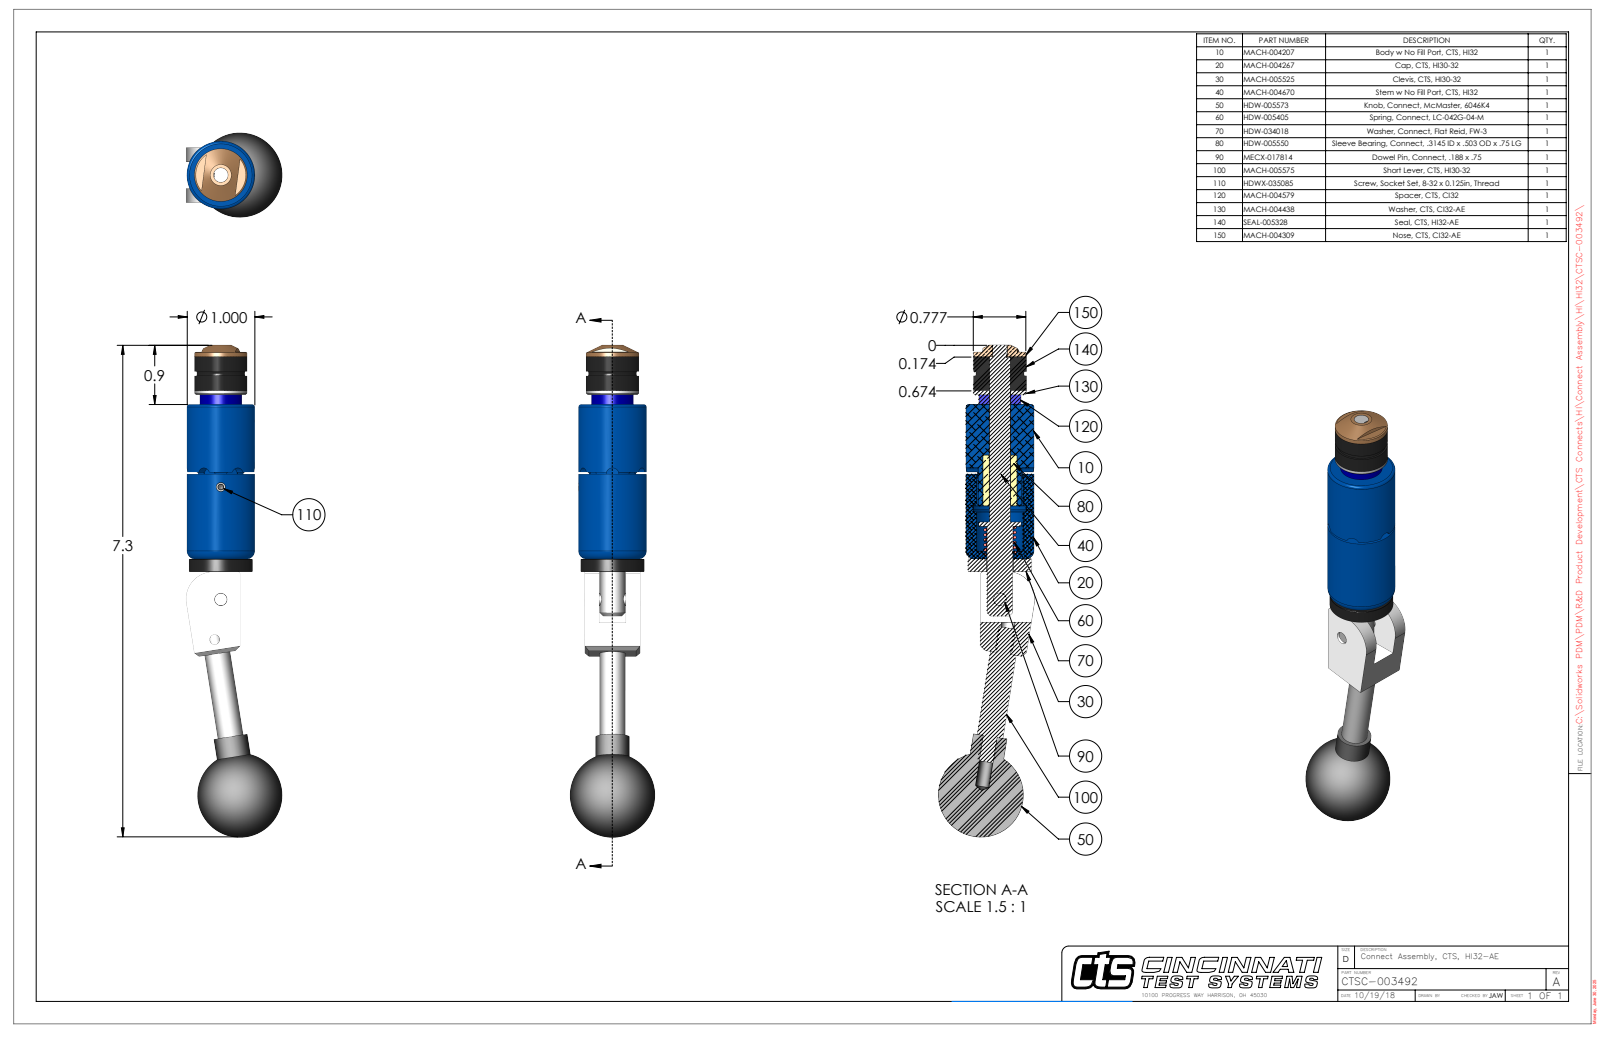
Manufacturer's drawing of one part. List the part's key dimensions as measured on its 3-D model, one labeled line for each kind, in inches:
Part name (STEP PRODUCT): CTSC-003492
STEP written by: SolidWorks 2023 (AUTOMOTIVE_DESIGN)
Units: inches
Bodies: 10 solids, 254 faces (97 planar, 100 cylindrical, 57 other)
Overall size (bounding box): 7.268 × 1.416 × 1.25
Volume: 4.009 in³ · Surface area: 34.63 in²
Round holes (diameter × count): ⌀0.201 ×2, ⌀0.136 ×1, ⌀0.15 ×1, ⌀0.189 ×1, ⌀0.213 ×1, ⌀0.31 ×1, ⌀0.314 ×1, ⌀0.316 ×1, ⌀0.385 ×1, ⌀0.392 ×1
Round bosses / shafts (diameter × count): ⌀0.25 ×2, ⌀0.201 ×2, ⌀1 ×1, ⌀0.936 ×1, ⌀0.777 ×1, ⌀0.618 ×1, ⌀0.5 ×1, ⌀0.38 ×1
Partial cylindrical surfaces — rounded edges, fillets, slot ends (radius × count): R0.093 ×6, R0.029 ×2, R0.344 ×1, R0.4 ×1, R0.467 ×1
Main face-to-face distances: 0.21, 0.602, 2.985, 0.5, 0.702, 2.283, 0.202, 2.485, 0.812, 3.172
Hole centre spacings: 0.599, 1.658, 2.252
